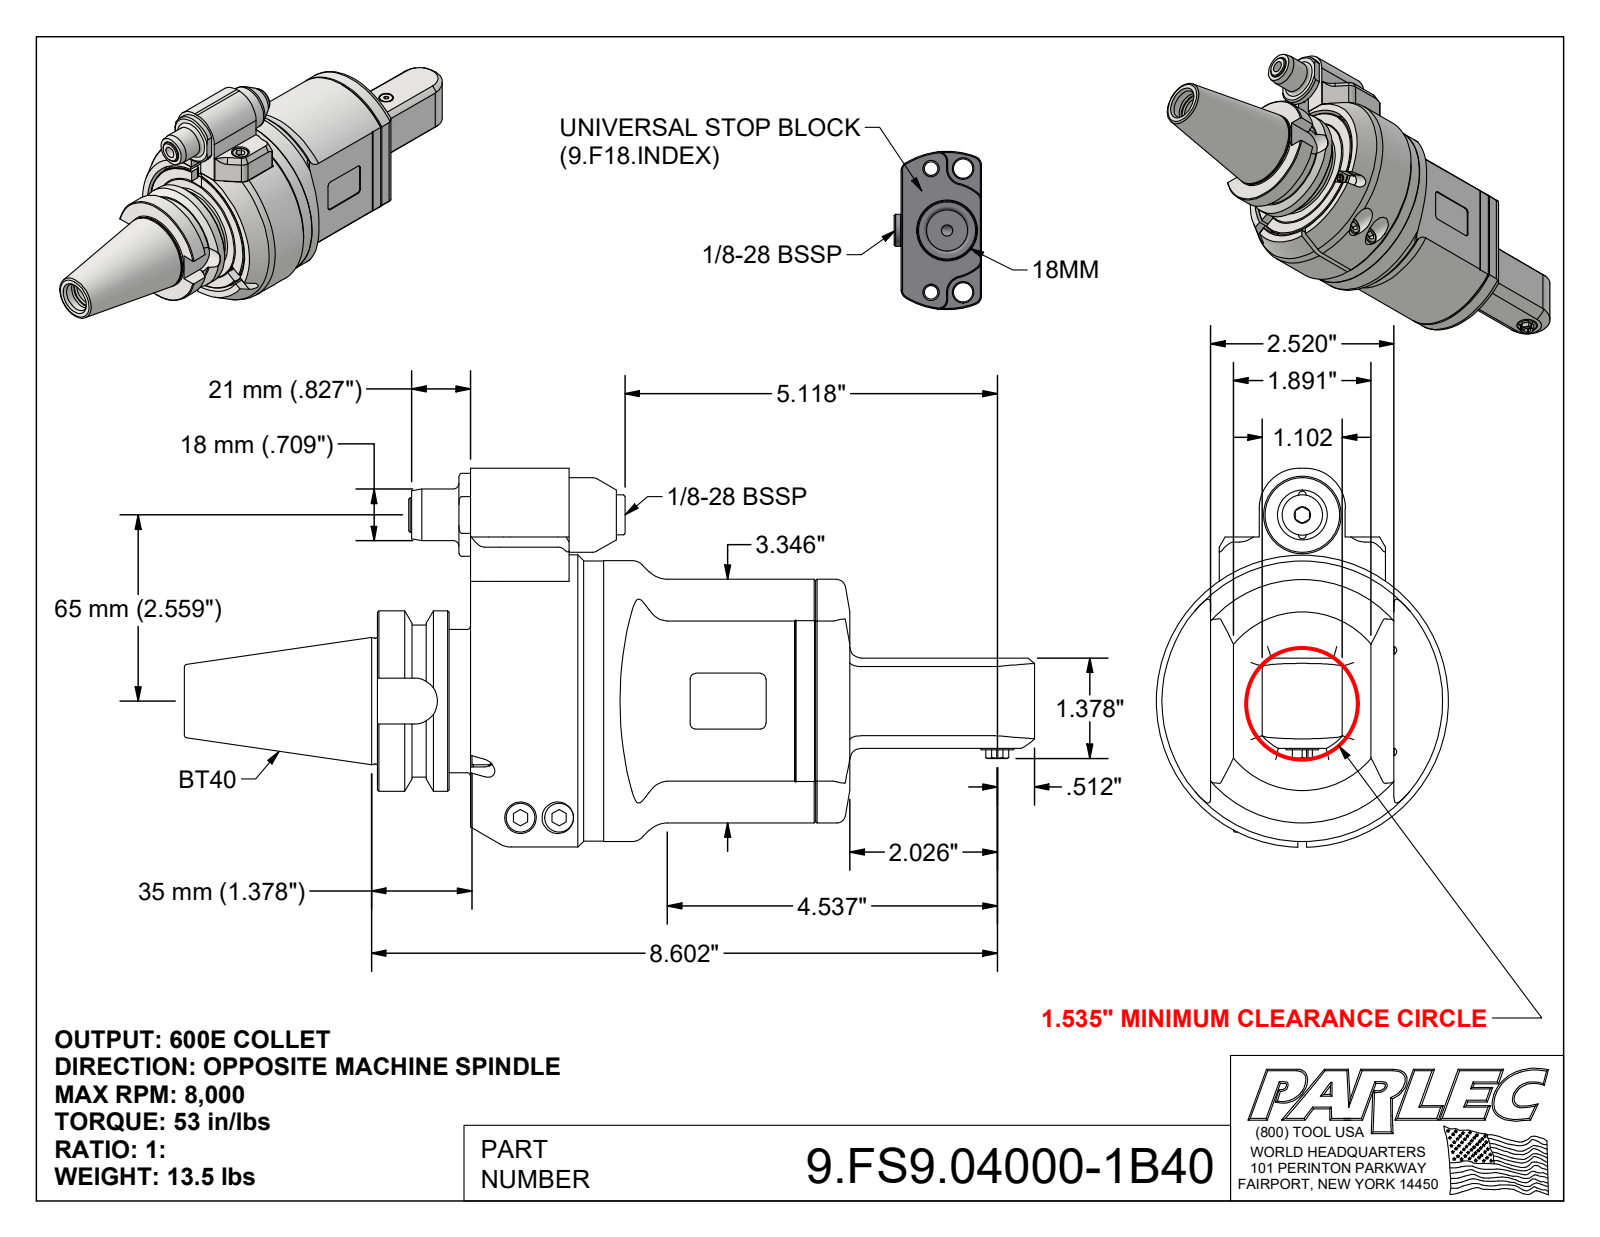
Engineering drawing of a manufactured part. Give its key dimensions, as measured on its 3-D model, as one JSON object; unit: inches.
{"part_name": "9.FS9.04000-1B40; 9_GA1_346; 9_FS9_04000", "step_written_by": "Autodesk Inventor 2025 (AUTOMOTIVE_DESIGN)", "units": "inches", "bodies": {"solids": 5, "faces": 491, "planar": 245, "cylindrical": 127, "other": 119}, "overall_size": [11.689, 5.206, 4.016], "volume_in3": 62.26, "surface_area_in2": 224.7, "round_holes": [[0.102, 2], [0.118, 2], [0.165, 2], [0.197, 2], [0.335, 2], [0.409, 2], [0.433, 2], [0.098, 1], [0.157, 1], [0.256, 1], [0.276, 1], [0.472, 1]], "round_bosses_or_shafts": [[0.394, 4], [0.236, 4], [0.315, 3], [0.709, 2], [0.098, 2], [4.016, 1], [3.858, 1], [3.85, 1]], "partial_cylinders_radius": [[0.079, 12], [0.157, 10], [0.551, 3], [0.02, 2], [0.039, 2], [0.138, 2], [0.197, 2], [0.118, 1]], "face_to_face_distances": [1.555, 0.295, 0.02, 1.258, 1.26, 0.709, 2.52, 0.315, 0.276, 1.28], "hole_center_spacings": [0.276, 0.512, 0.551, 1.081, 1.72, 2.283, 2.323, 2.559]}
